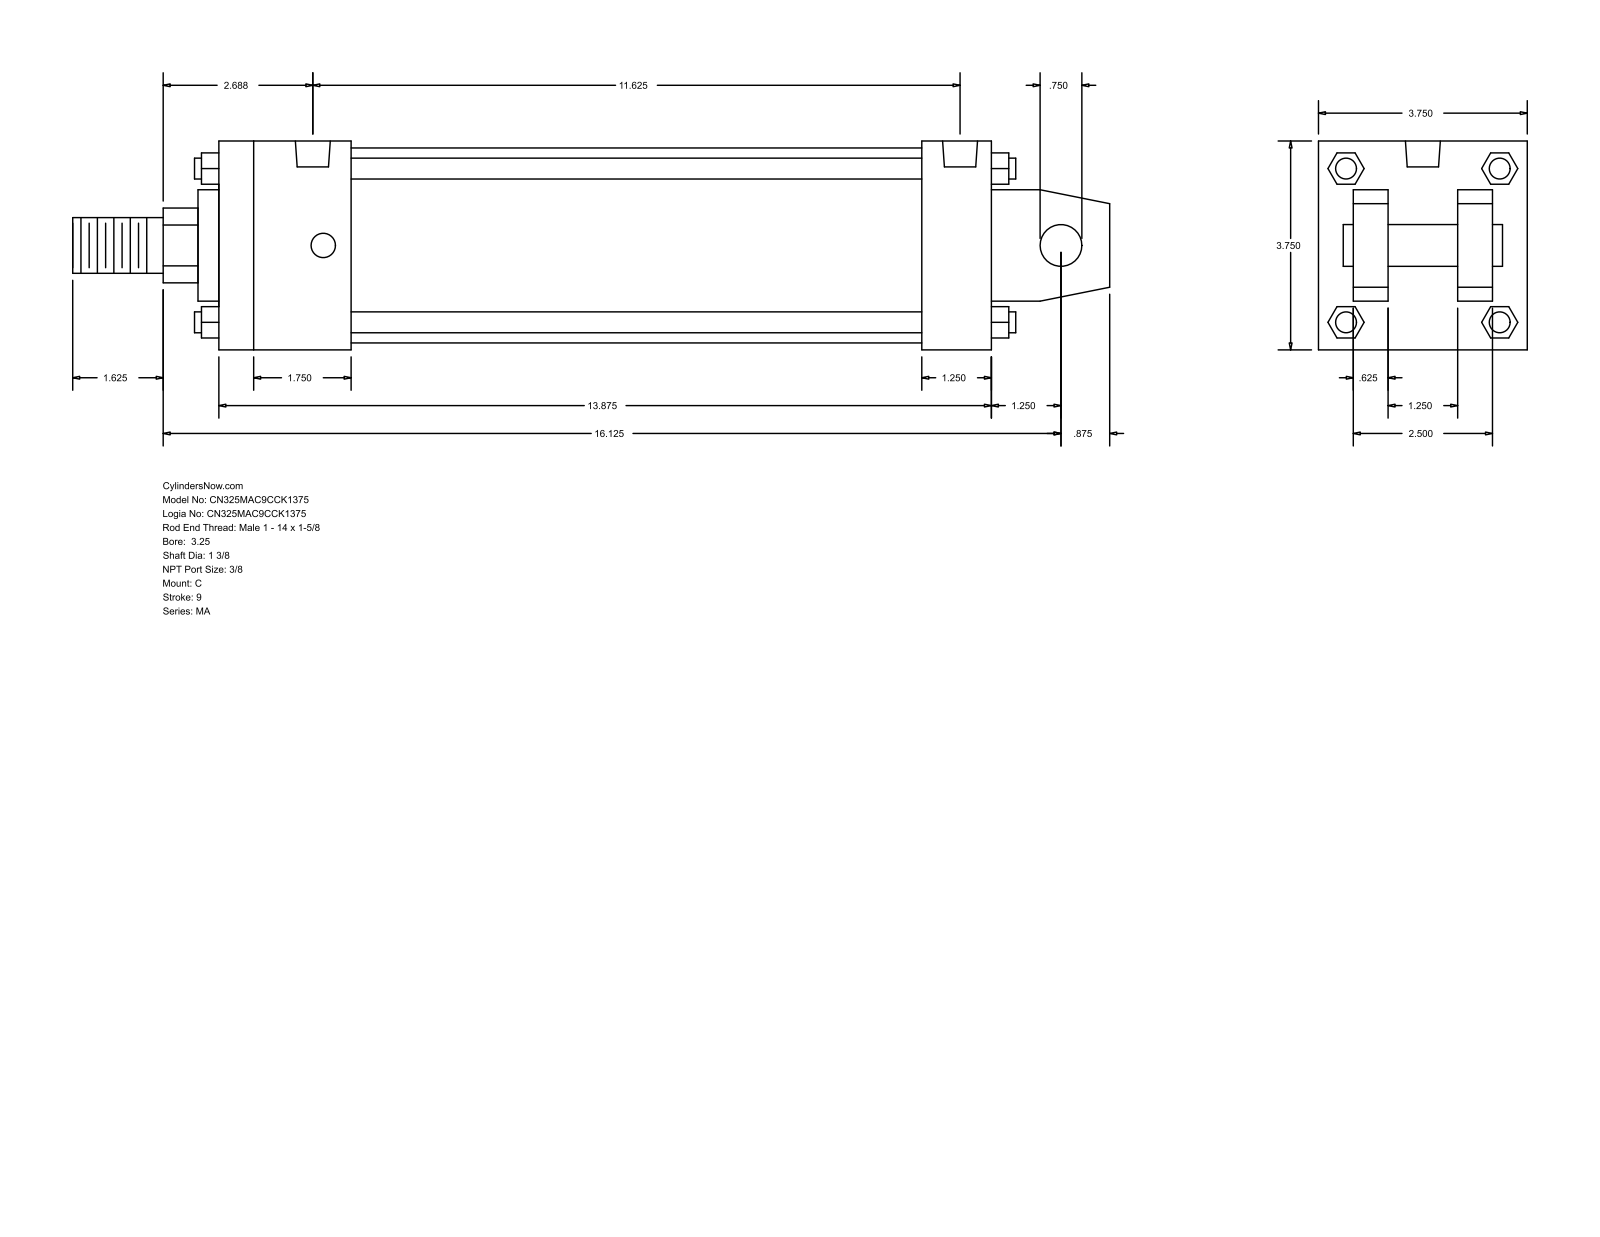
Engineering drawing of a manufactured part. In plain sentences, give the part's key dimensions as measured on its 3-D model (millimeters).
The part is named "MA_C__0325_1.375". Its 3-D file was written by "GSSL Pune (CONFIG_CONTROL_DESIGN)". It is 0 solids with 139 faces: 108 planar, 31 cylindrical and 0 other. Overall it measures 473.07 by 95.25 by 95.25 millimeters. Round holes: 4 of diameter 11.11, 2 of diameter 15.93. Round bosses or shafts: 4 of diameter 9.53, 1 of diameter 88.9, 1 of diameter 50.8, 1 of diameter 34.92, 1 of diameter 25.4, 1 of diameter 19.05. Partial cylindrical surfaces (rounded edges, fillets, slot ends): 1 of radius 17.06. The main face-to-face distances are 95.24, 15.87, 63.5, 352.42, 31.74, 79.37, 47.63, 320.67, 31.75, 60.32. The hole center spacings are 4.77, 285.74, 290.51, 295.28.
